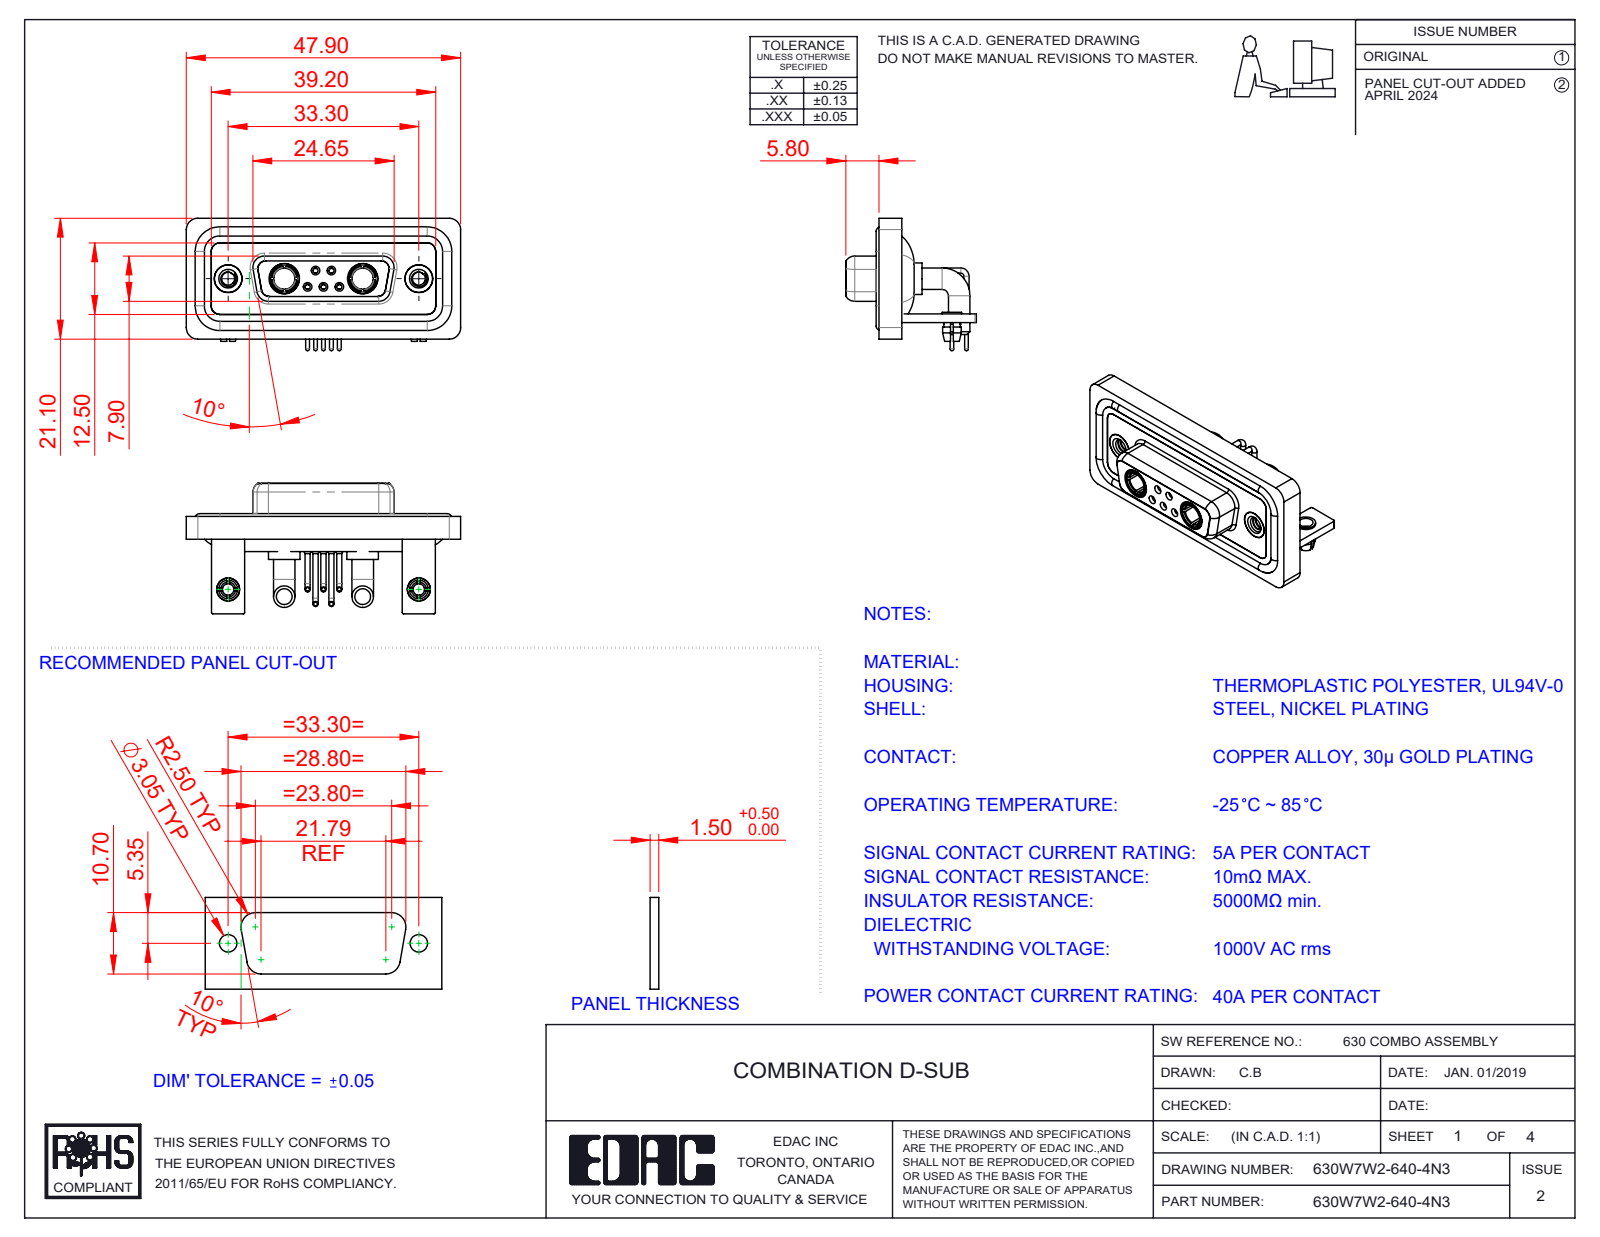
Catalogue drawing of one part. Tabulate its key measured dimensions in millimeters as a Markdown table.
| quantity | value |
| --- | --- |
| part name | 630Combo Contact Row 2_50 Contacts; 630Combo Waterproof Housing_15 Contacts; 630Combo Board Lock_50 Contacts; 630Combo Shell Front_15 Contacts (+7 more) |
| STEP written by | SolidWorks 2023 (CONFIG_CONTROL_DESIGN) |
| units | millimeters |
| bodies | 20 solids, 947 faces (306 planar, 409 cylindrical, 232 other) |
| overall size | 47.9 × 23.12 × 22.8 |
| volume | 6 744 mm³ |
| surface area | 11 239 mm² |
| round holes (diameter × count) | 2 × 7, 0.9 × 5, 1.1 × 5, 1.5 × 5, 4.85 × 4, 1.6 × 3, 1.7 × 2, 2.26 × 2, 2.5 × 2, 3.2 × 2, 3.7 × 2, 4 × 2 |
| round bosses / shafts (diameter × count) | 1.6 × 6, 0.9 × 5, 0.65 × 5, 3.75 × 4, 5.5 × 2, 5.2 × 2, 4.96 × 2, 4.95 × 2 |
| partial cylindrical surfaces (radius × count) | 2 × 21, 1.5 × 18, 0.25 × 16, 1.35 × 12, 1.6 × 8, 0.5 × 5, 0.6 × 4, 0.65 × 4 |
| main face-to-face distances | 0.4, 2.9, 1.5, 1.8, 3.7, 1.1, 4.1, 1.6, 2.5, 1.4 |
| hole center spacings | 3.16, 2.77, 9.8, 23.5, 33.3, 4.31, 4.33, 5.03 |
